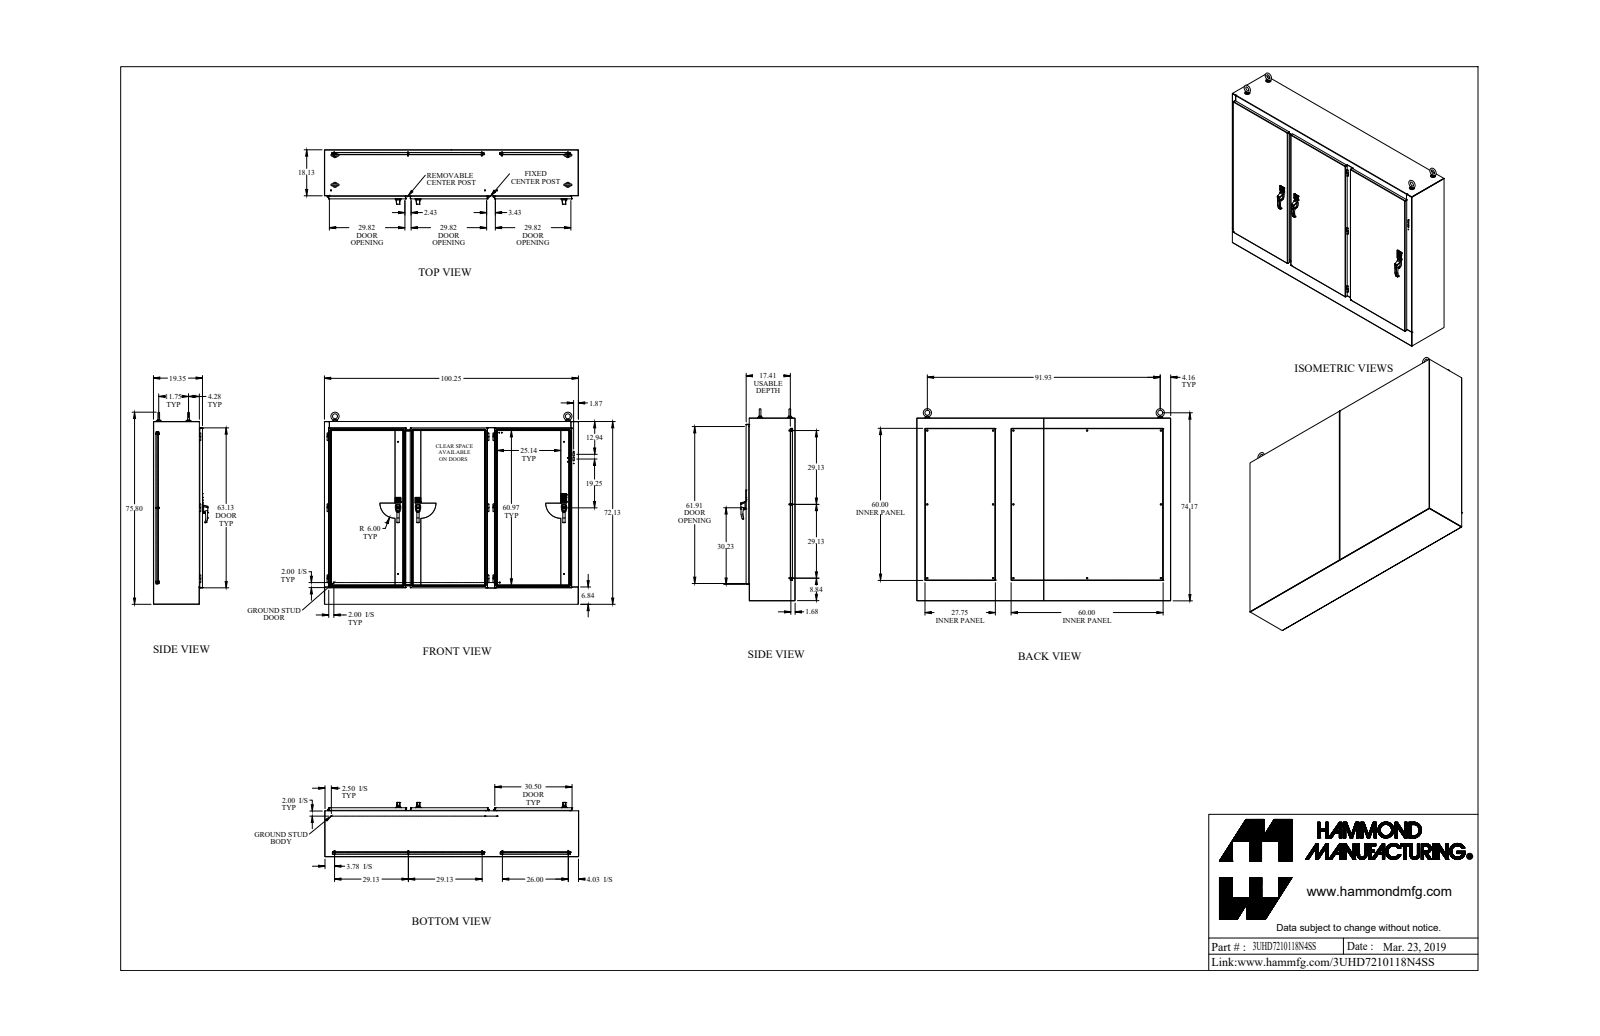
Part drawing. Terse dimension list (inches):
name: 3UHD7210118N4SS
written by: SolidWorks 2018 (AUTOMOTIVE_DESIGN)
unit: in
bodies: 309 solids, 4520 faces (2746 planar, 1283 cylindrical, 491 other)
size: 100.25 × 75.799 × 21.464
volume: 2 548 in³; area: 65 573 in²
holes: 22× ⌀0.25, 20× ⌀0.196, 14× ⌀0.307, 10× ⌀0.281, 9× ⌀0.313, 9× ⌀0.35, 9× ⌀0.445, 8× ⌀0.875, 6× ⌀0.156, 6× ⌀0.266, 6× ⌀0.39, 5× ⌀0.445
bosses: 20× ⌀1, 17× ⌀0.25, 14× ⌀0.65, 14× ⌀0.375, 14× ⌀0.332, 10× ⌀0.246, 9× ⌀0.625, 7× ⌀0.486
rounds: 68× R0.125, 48× R0.017, 41× R0.048, 41× R0.143, 40× R0.06, 36× R0.5, 32× R0.25, 20× R0.185
face distances: 0.095, 0.046, 19.368, 19.273, 19.322, 19.227, 0.047, 1.907, 1.812, 17.415
hole spacings: 65.5, 1, 2.126, 7.87, 11.75, 57.63, 91.934, 91.959
